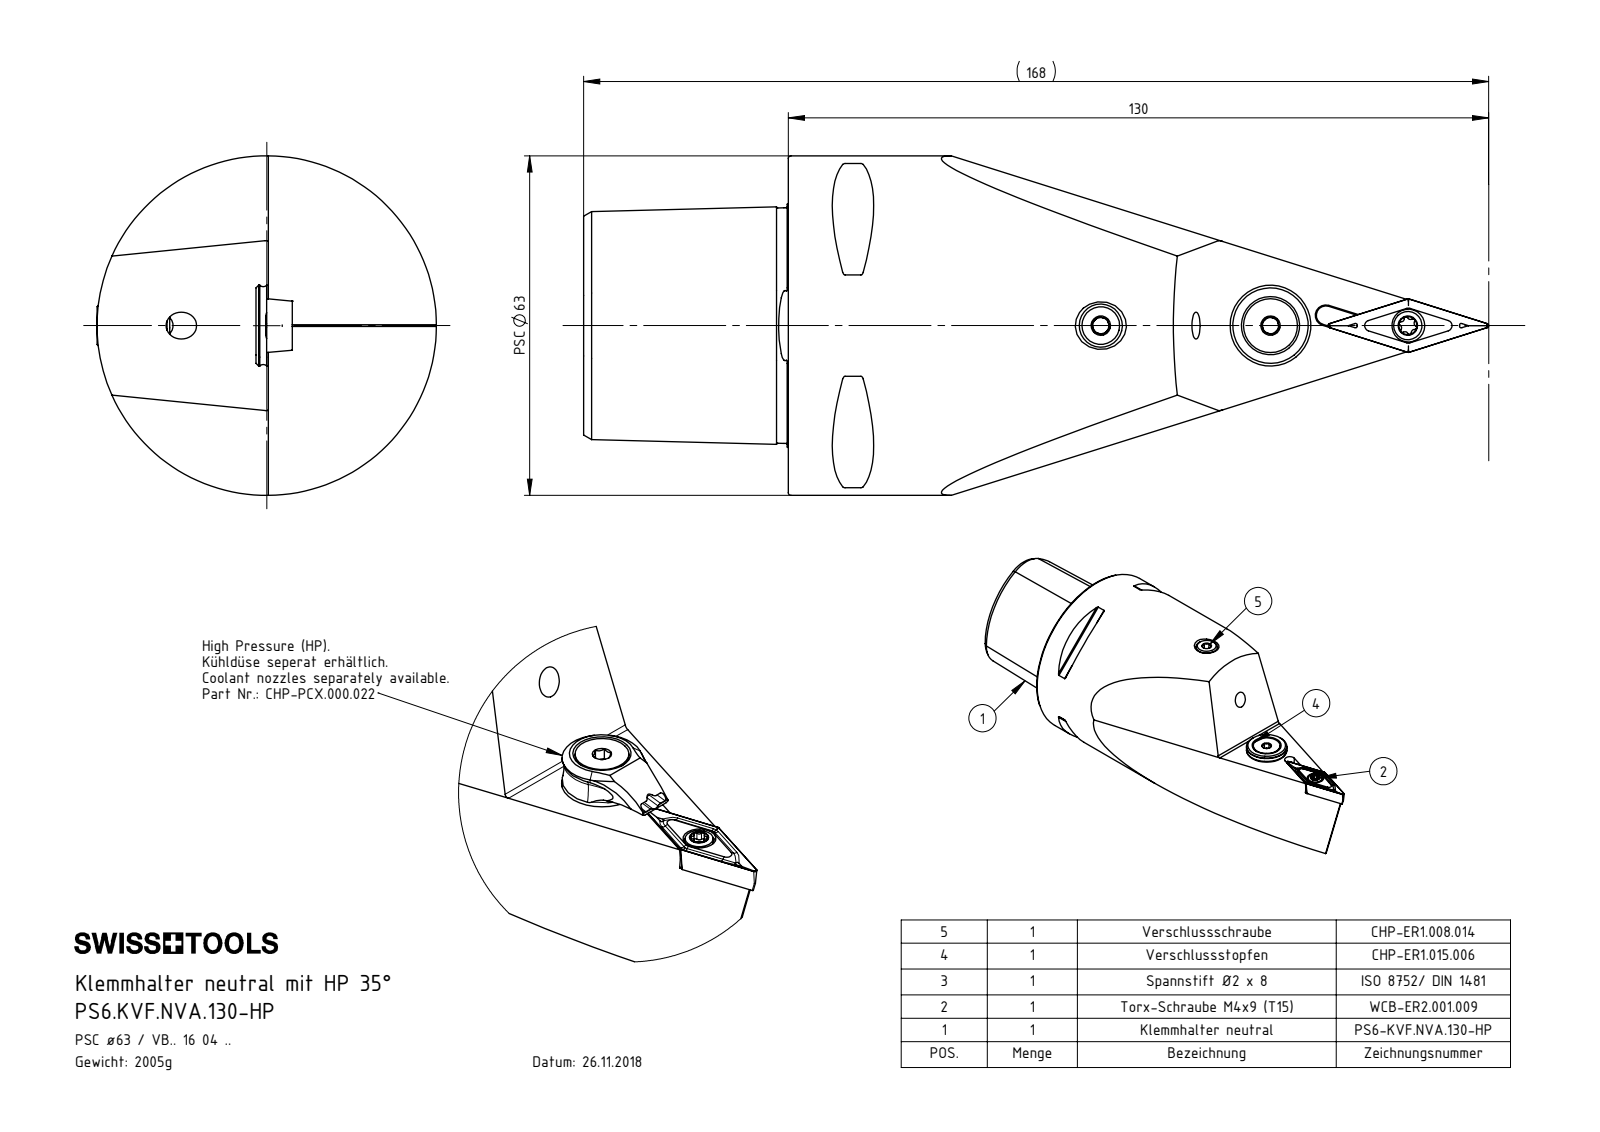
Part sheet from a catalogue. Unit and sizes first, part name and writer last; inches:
Units: inches
Overall size (bounding box): 6.614 × 2.48 × 2.48
Round holes (diameter × count): ⌀0.165 ×2, ⌀0.197 ×2, ⌀0.047 ×1, ⌀0.079 ×1, ⌀0.098 ×1, ⌀0.118 ×1, ⌀0.13 ×1, ⌀0.157 ×1, ⌀0.173 ×1, ⌀0.205 ×1, ⌀0.24 ×1, ⌀0.276 ×1
Round bosses / shafts (diameter × count): ⌀2.48 ×1, ⌀0.591 ×1, ⌀0.528 ×1, ⌀0.394 ×1, ⌀0.315 ×1, ⌀0.217 ×1, ⌀0.207 ×1, ⌀0.197 ×1
Partial cylindrical surfaces — rounded edges, fillets, slot ends (radius × count): R0.02 ×8, R0.013 ×6, R0.023 ×6, R0.006 ×2, R0.236 ×2, R0.069 ×1
Main face-to-face distances: 1.496, 0.98, 0.176, 0.165, 1.063, 0.433, 2.197, 0.425, 1.488, 0.262
Hole centre spacings: 0.177, 0.873, 0.877, 1.004, 1.007, 1.083, 1.24, 1.382
Volume: 15.55 in³ · Surface area: 60.14 in²
Bodies: 8 solids, 374 faces (90 planar, 99 cylindrical, 185 other)
Part name (STEP PRODUCT): DIN 3771 - 13x1; CHP-ER1.015.006; CHP-ER1.008.014_A; ISO 8752 2x8 (+6 more)
STEP written by: SolidWorks 2017 (AUTOMOTIVE_DESIGN)
